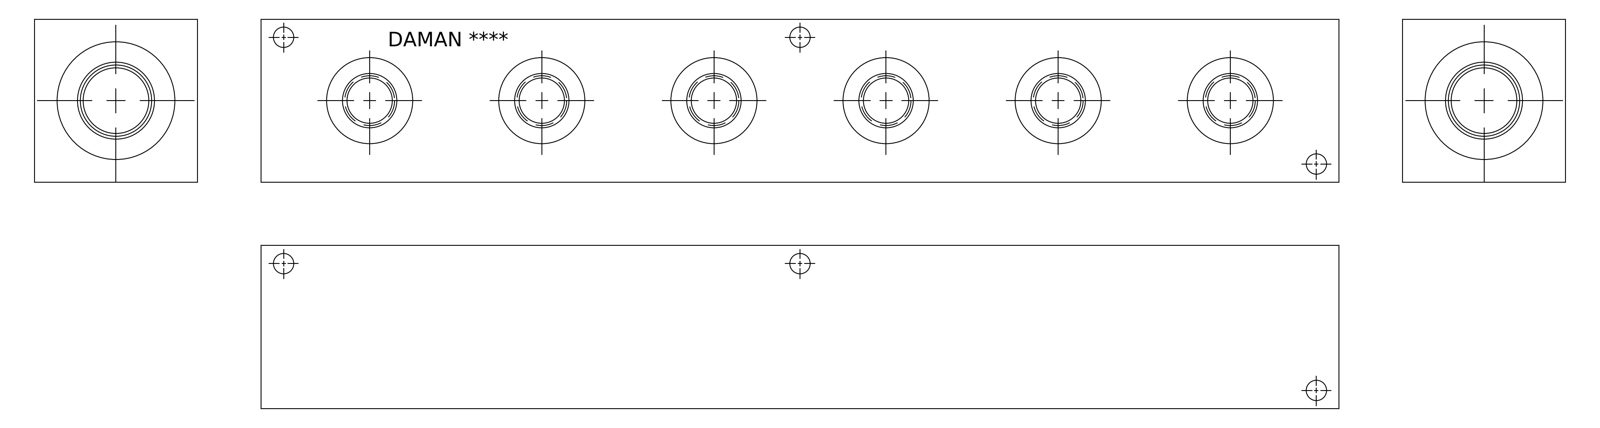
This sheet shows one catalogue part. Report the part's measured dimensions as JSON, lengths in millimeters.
{"part_name": "Part_AH0000608S_3D", "step_written_by": "Autodesk Inventor 2019 (AUTOMOTIVE_DESIGN)", "units": "millimeters", "bodies": {"solids": 1, "faces": 415, "planar": 213, "cylindrical": 50, "other": 152}, "overall_size": [377.82, 57.15, 57.15], "volume_mm3": 1146000, "surface_area_mm2": 112393, "round_holes": [[7.14, 6], [17.5, 6], [19.05, 6], [19.25, 6], [30.63, 6], [15.88, 4], [23.01, 1], [24.92, 1], [26.99, 1], [27, 1], [27.43, 1], [42.04, 1]], "face_to_face_distances": [57.15, 0.79, 56.36, 377.82, 0.78, 377.04, 376.25, 377.03, 42.09, 14.27], "hole_center_spacings": [60.33, 120.65, 37.45, 37.48, 60.32, 93.16, 152.43, 152.46]}
